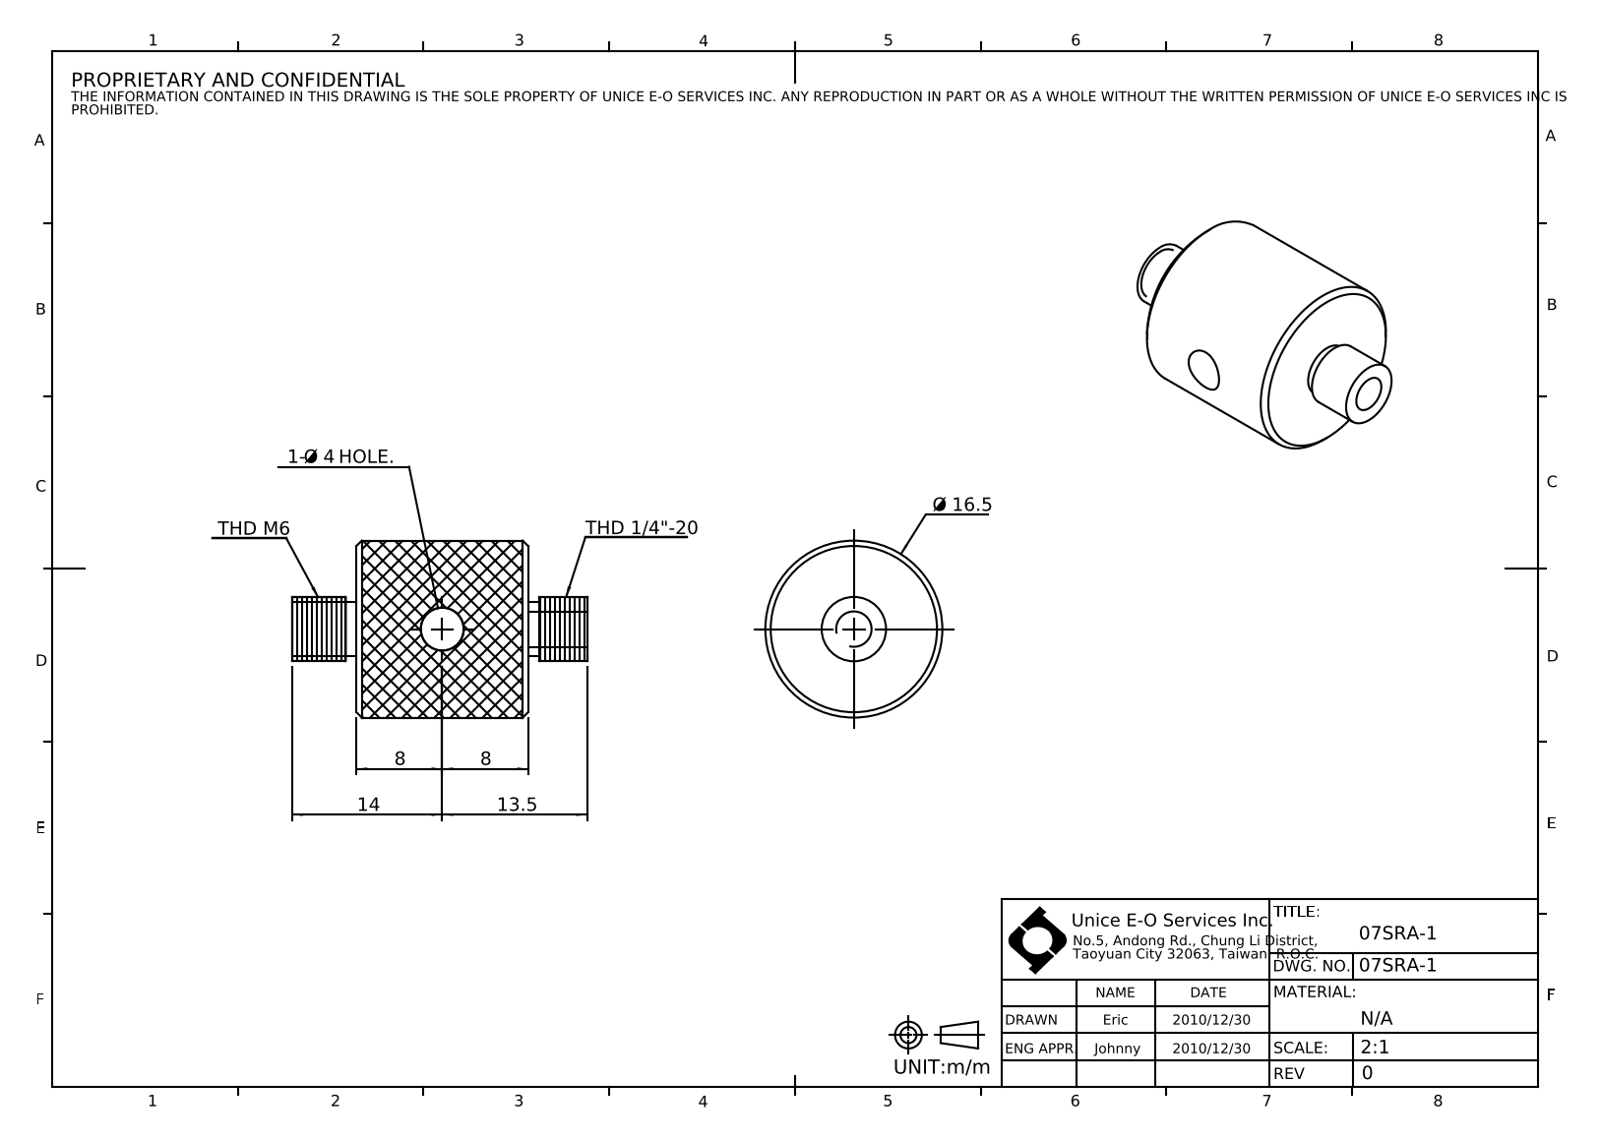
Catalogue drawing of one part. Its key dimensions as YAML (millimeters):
part_name: "07SRA-1"
step_written_by: "SolidWorks 2016 (CONFIG_CONTROL_DESIGN)"
units: millimeters
bodies: {solids: 1, faces: 22, planar: 6, cylindrical: 12, other: 4}
overall_size: [27.5, 16.5, 16.5]
volume: 3511
surface_area: 1650
round_holes:
  - {diameter: 4, count: 1}
round_bosses_or_shafts:
  - {diameter: 16.5, count: 1}
  - {diameter: 6, count: 1}
  - {diameter: 5, count: 1}
face_to_face_distances: [16, 5.5, 21.5, 27.5, 22, 6, 1, 17, 4.5, 22.5]
